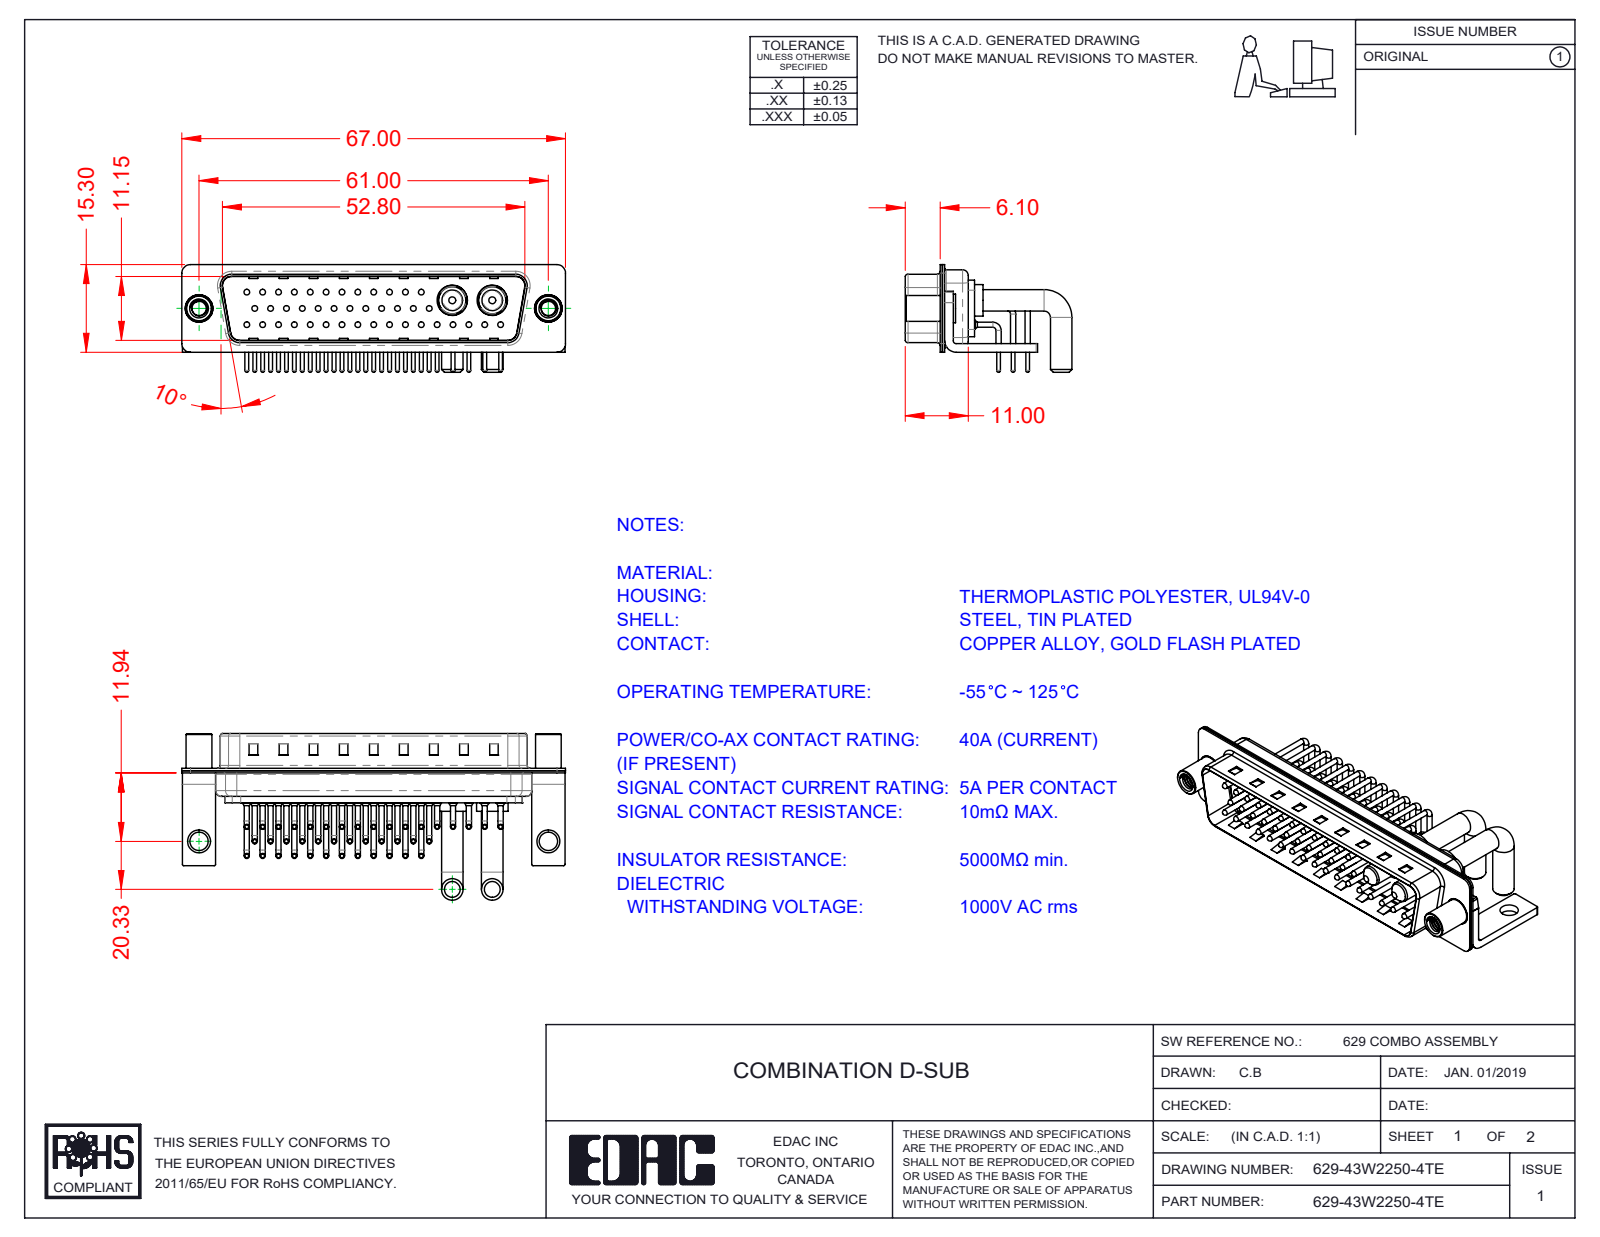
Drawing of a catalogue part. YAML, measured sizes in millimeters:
part_name: "629Combo Threaded Standoff_D; Power Pin_Ext 40A RA 50; 629Combo Contact Row 3; 629-43W2250-4TE (+6 more)"
step_written_by: "SolidWorks 2020 (CONFIG_CONTROL_DESIGN)"
units: millimeters
bodies: {solids: 52, faces: 5106, planar: 2869, cylindrical: 1731, other: 506}
overall_size: [67, 29.11, 18.8]
volume: 5994
surface_area: 13898
round_holes:
  - {diameter: 0.75, count: 41}
  - {diameter: 1.6, count: 41}
  - {diameter: 2, count: 41}
  - {diameter: 2.5, count: 2}
  - {diameter: 3.2, count: 2}
  - {diameter: 4, count: 2}
  - {diameter: 4.8, count: 2}
  - {diameter: 4.85, count: 2}
  - {diameter: 5.3, count: 2}
round_bosses_or_shafts:
  - {diameter: 0.9, count: 82}
  - {diameter: 1.5, count: 41}
  - {diameter: 1, count: 41}
  - {diameter: 0.65, count: 41}
  - {diameter: 3.75, count: 4}
  - {diameter: 5.5, count: 2}
  - {diameter: 5.2, count: 2}
  - {diameter: 5, count: 2}
partial_cylinders:
  - {radius: 1.01, count: 41}
  - {radius: 0.25, count: 16}
  - {radius: 1.5, count: 16}
  - {radius: 2, count: 13}
  - {radius: 0.5, count: 9}
  - {radius: 1.6, count: 8}
  - {radius: 0.6, count: 4}
  - {radius: 0.65, count: 4}
face_to_face_distances: [0.4, 1.5, 11.55, 5.6, 5.2, 0.8, 1.9, 4.1, 6, 0.78]
hole_center_spacings: [2.77, 5.54, 3.16, 8.31, 11.08, 13.85, 16.62, 19.39]
